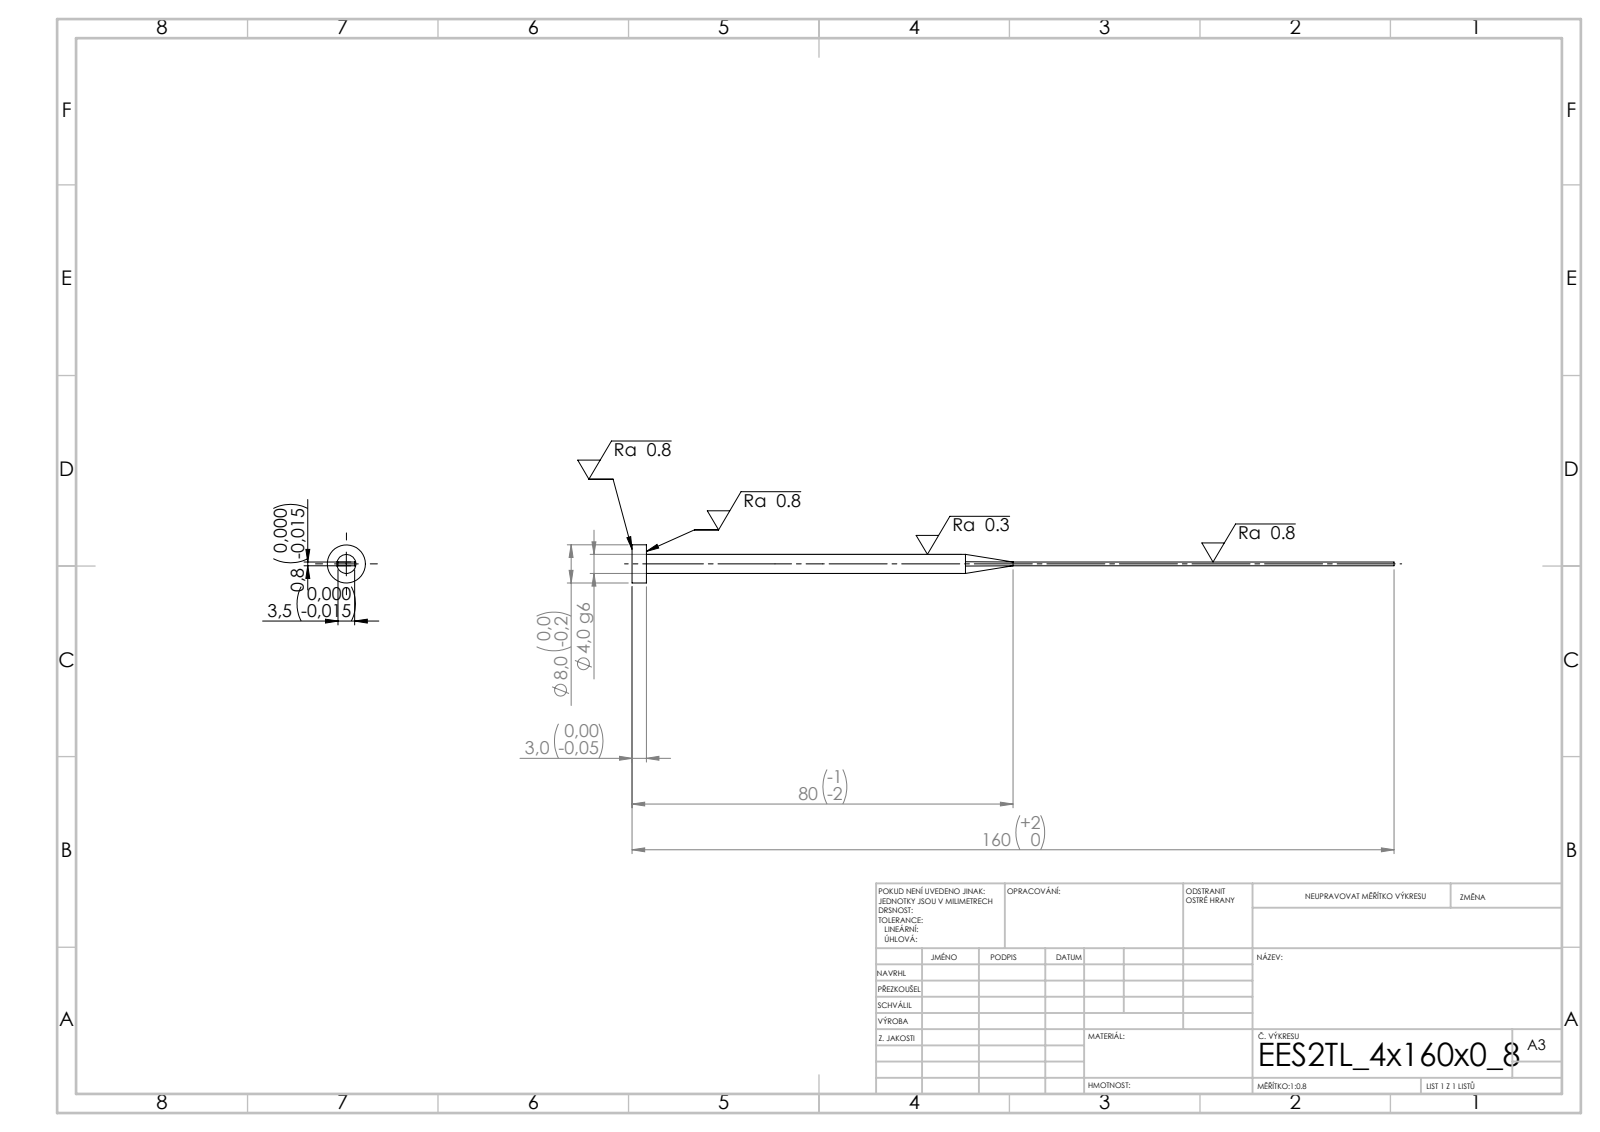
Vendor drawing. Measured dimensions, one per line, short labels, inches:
written by: SolidWorks 2019 (CONFIG_CONTROL_DESIGN)
unit: in
bodies: 1 solid, 15 faces (7 planar, 4 cylindrical, 4 other)
size: 6.299 × 0.315 × 0.315
volume: 0.079 in³; area: 2.787 in²
bosses: 1× ⌀0.315, 1× ⌀0.157
face distances: 0.031, 0.138, 0.118, 6.299, 6.181
